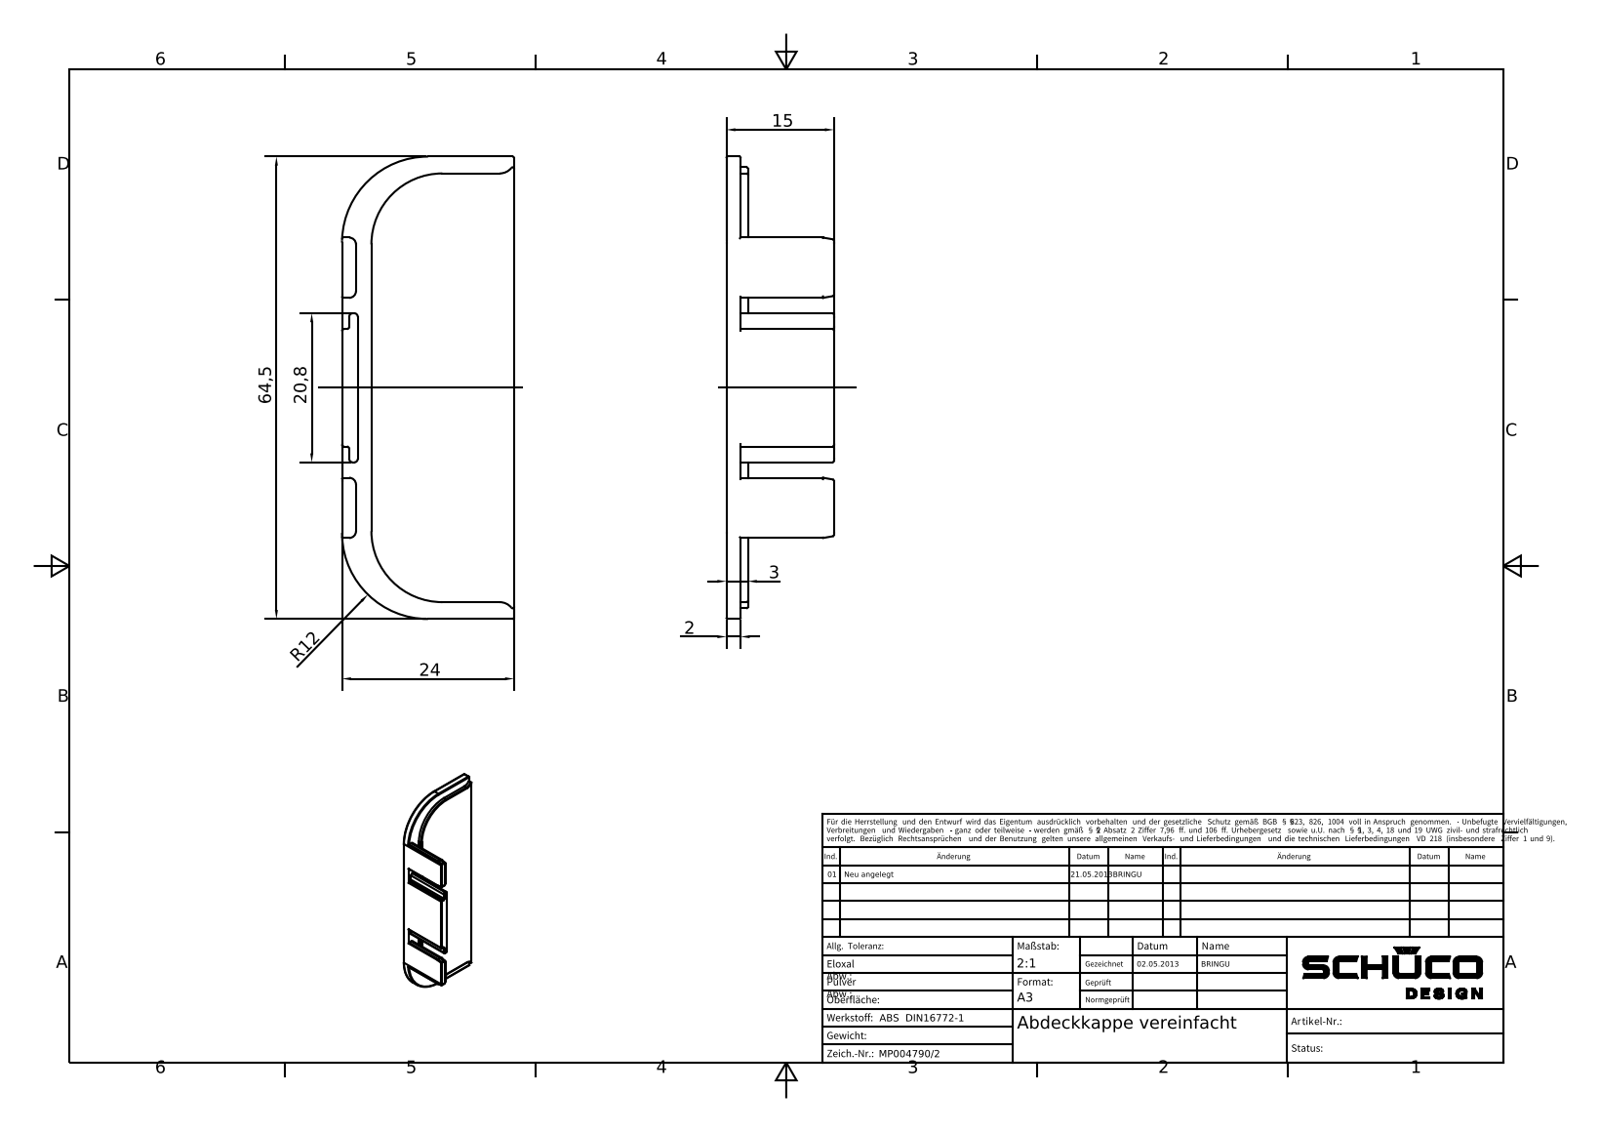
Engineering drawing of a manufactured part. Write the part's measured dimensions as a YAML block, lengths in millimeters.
part_name: "MP004790"
step_written_by: "Autodesk Inventor 2024 (AUTOMOTIVE_DESIGN)"
units: millimeters
bodies: {solids: 1, faces: 124, planar: 32, cylindrical: 55, other: 37}
overall_size: [64.5, 24, 15]
volume: 5064
surface_area: 4504
partial_cylinders:
  - {radius: 0.2, count: 33}
  - {radius: 0.3, count: 4}
  - {radius: 0.5, count: 4}
  - {radius: 0.95, count: 4}
  - {radius: 2.1, count: 2}
  - {radius: 9.9, count: 2}
  - {radius: 12, count: 2}
face_to_face_distances: [3, 1, 2.2, 2, 24, 21.8, 1.95, 22.05, 15, 13]
